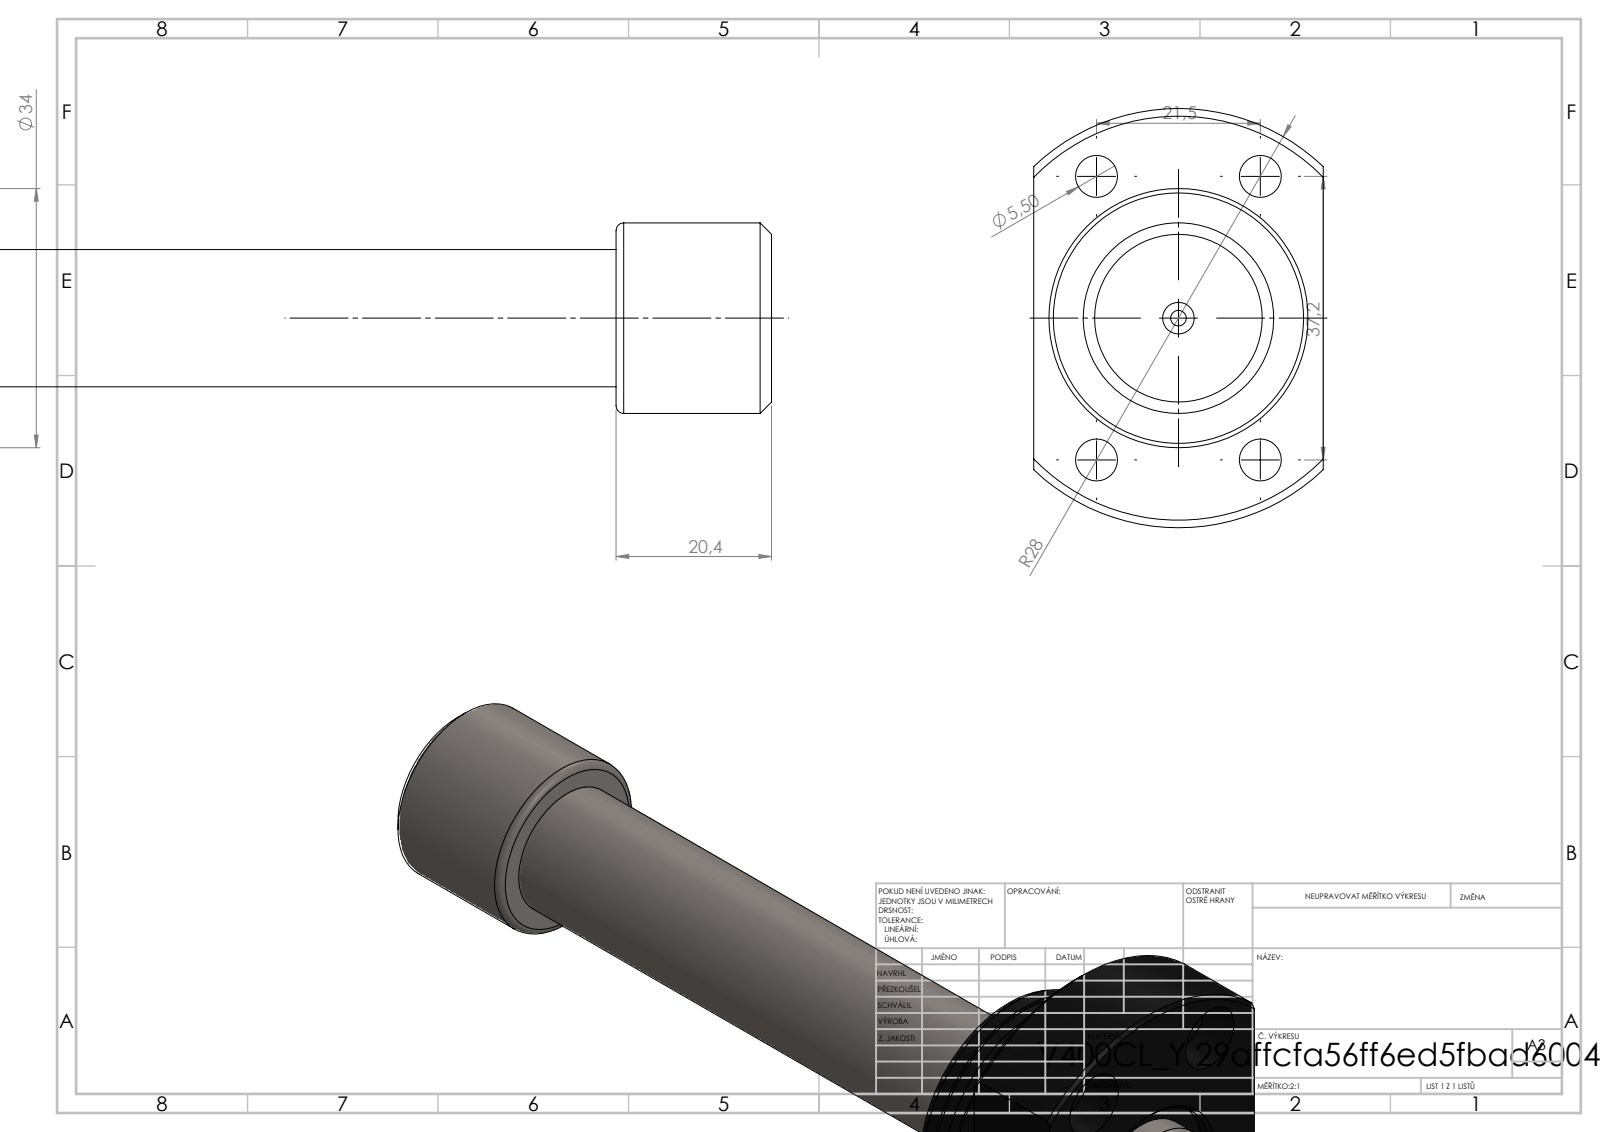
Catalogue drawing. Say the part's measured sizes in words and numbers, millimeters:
The part is named "V400CL_VC_X; V400CL_PC_Y". Its 3-D file was written by "SolidWorks 2019 (CONFIG_CONTROL_DESIGN)". It is 2 solids with 103 faces: 26 planar, 47 cylindrical and 30 other. Overall it measures 135 by 55 by 38 millimeters. Its volume is 66 974 cubic millimeters and its surface area 18 837 square millimeters. Round holes: 4 of diameter 5.5, 4 of diameter 9, 1 of diameter 2.05, 1 of diameter 5, 1 of diameter 6, 1 of diameter 18, 1 of diameter 22.5. Round bosses or shafts: 1 of diameter 34, 1 of diameter 33, 1 of diameter 25. Partial cylindrical surfaces (rounded edges, fillets, slot ends): 1 of radius 8.75, 1 of radius 27.5. The main face-to-face distances are 14, 38, 12.5, 26.5, 102.45, 114.95, 128.95, 2, 3.5, 135. The hole center spacings are 21.48, 21.5, 37.2, 42.97.
